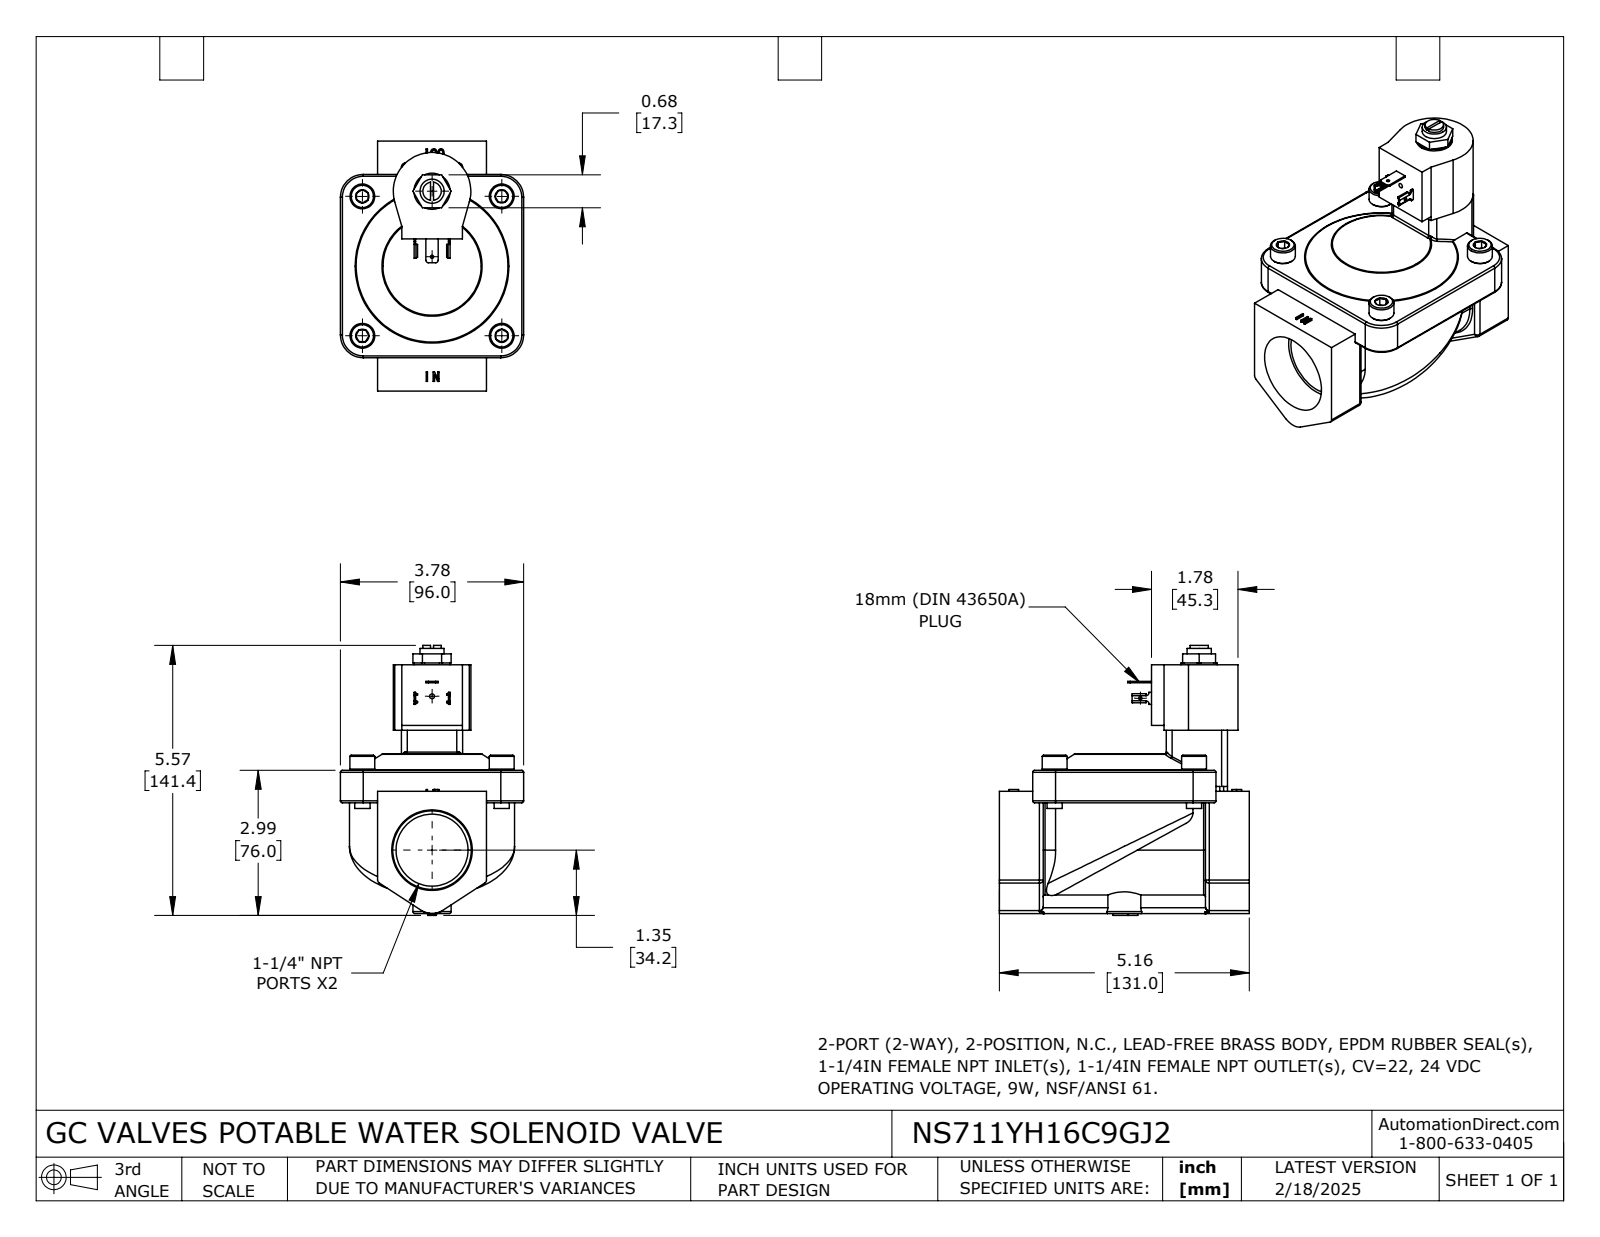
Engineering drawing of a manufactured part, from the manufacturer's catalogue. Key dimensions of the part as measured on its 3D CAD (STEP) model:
Part name (STEP PRODUCT): NS711YH16C9GJ2
STEP written by: SolidWorks 2024 (CONFIG_CONTROL_DESIGN)
Units: millimetres
Bodies: 1 solid, 442 faces (201 planar, 115 cylindrical, 126 other)
Overall size (bounding box): 141.37 × 131 × 96
Volume: 569 832 mm³ · Surface area: 69 550 mm²
Round holes (diameter × count): ⌀1.68 ×1, ⌀1.7 ×1, ⌀2.53 ×1, ⌀30.48 ×1, ⌀37.69 ×1
Round bosses / shafts (diameter × count): ⌀13 ×4, ⌀8 ×4, ⌀18.95 ×1, ⌀12.67 ×1, ⌀9.65 ×1
Partial cylindrical surfaces — rounded edges, fillets, slot ends (radius × count): R2 ×14, R1 ×13, R3 ×6, R0.15 ×4, R1.04 ×4, R12 ×4, R0.2 ×2, R1.27 ×2
Main face-to-face distances: 19.5, 32, 11, 6, 76.5, 8.5, 96, 17, 25.5, 12.5
Hole centre spacings: 34.29, 80.56
